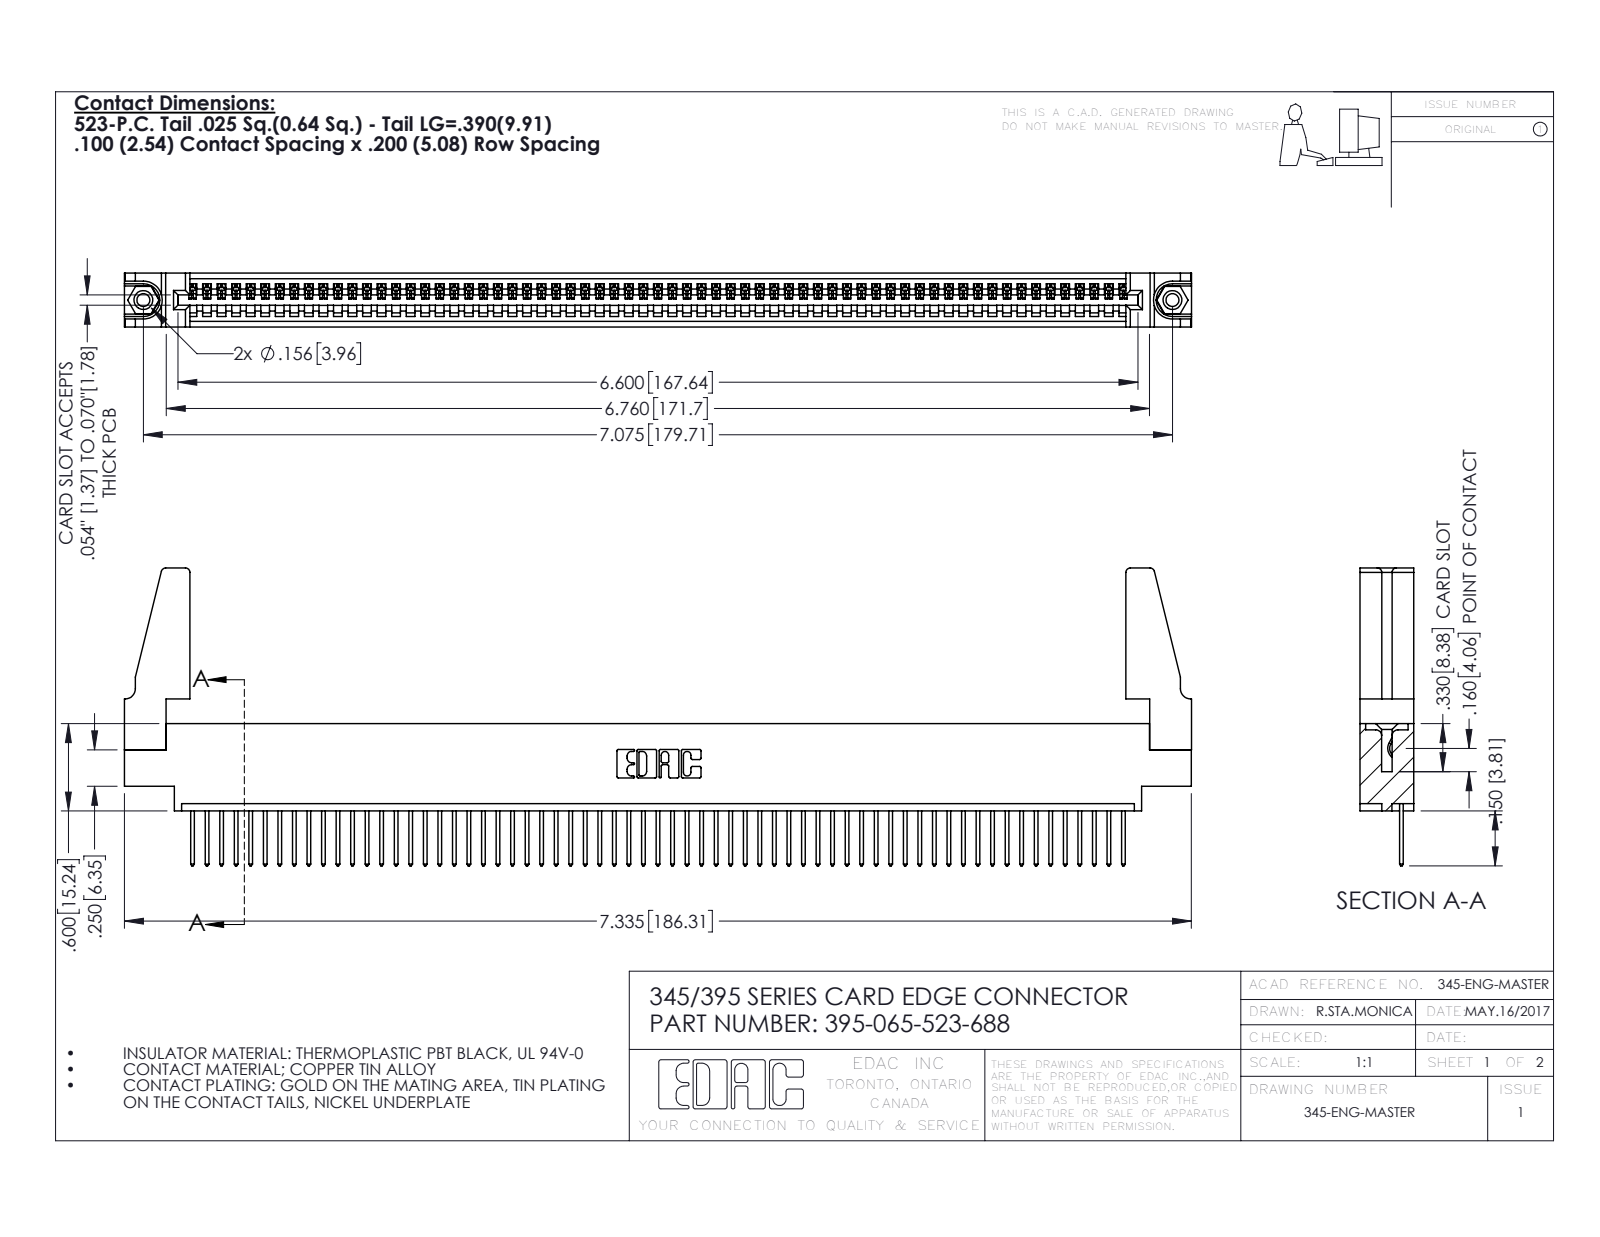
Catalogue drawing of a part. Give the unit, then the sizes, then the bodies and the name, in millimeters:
Units: millimetres
Overall size (bounding box): 186.3 × 52 × 9.4
Round holes (diameter × count): ⌀2.3 ×2, ⌀3.2 ×2, ⌀4 ×2, ⌀1.6 ×1
Round bosses / shafts (diameter × count): ⌀3.9 ×2
Partial cylindrical surfaces — rounded edges, fillets, slot ends (radius × count): R0.2 ×130, R0.3 ×130, R0.3 ×22, R0.8 ×8, R0.2 ×6, R0.8 ×6, R0.7 ×3, R0.8 ×2
Main face-to-face distances: 1.8, 7.6, 9.4, 2.5, 6.9, 0.6, 5.1, 5.7, 4.4, 3.8
Hole centre spacings: 6.9, 173.7, 179.7
Volume: 21 010 mm³ · Surface area: 27 230 mm²
Bodies: 70 solids, 4024 faces (2756 planar, 1252 cylindrical, 16 other)
Part name (STEP PRODUCT): 345-250-001_345-250-001-102; 345-292-001_345-293-123; 395-065-523-688; 345-220-078_345-220-088 (+1 more)
STEP written by: SolidWorks 2016 (CONFIG_CONTROL_DESIGN)
